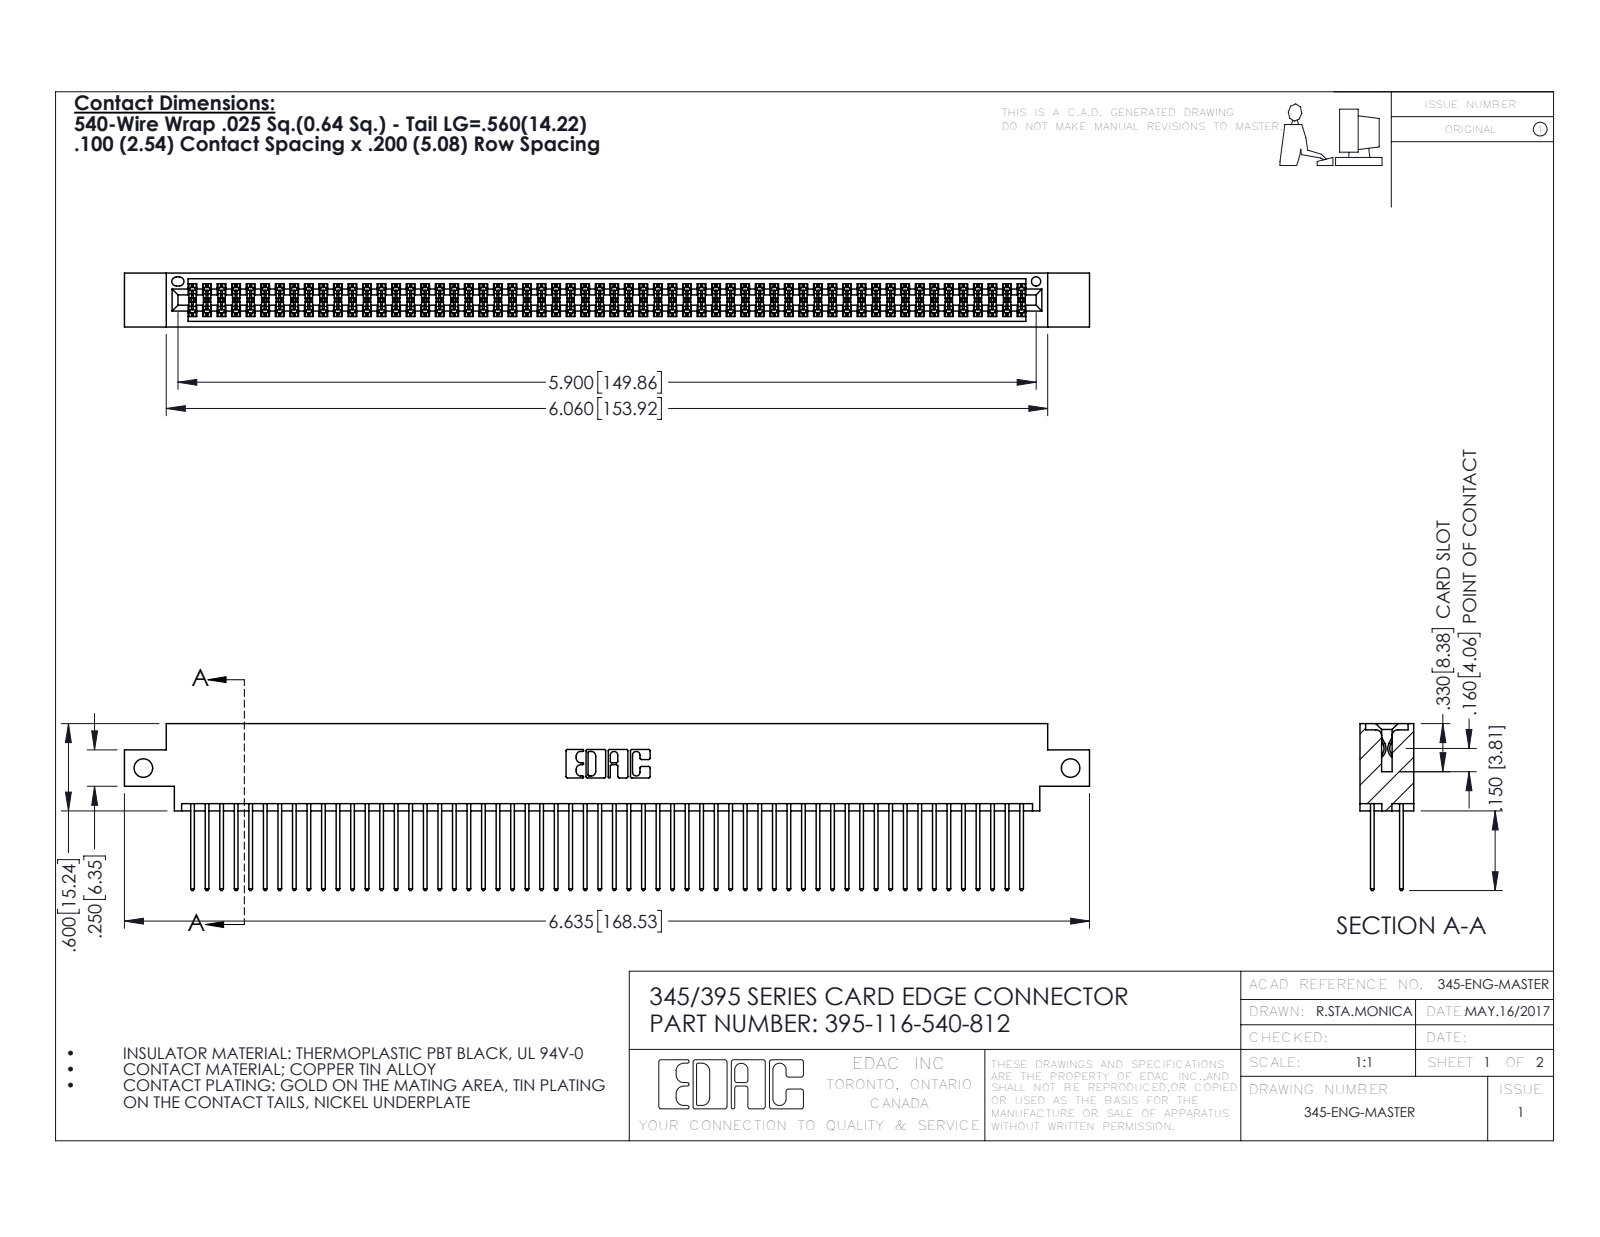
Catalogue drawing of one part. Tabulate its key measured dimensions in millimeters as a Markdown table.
| quantity | value |
| --- | --- |
| part name | 345-292-001_345-293-140; 345 Part_0.170 Offset - Side Mount; 395-116-540-812 |
| STEP written by | SolidWorks 2016 (CONFIG_CONTROL_DESIGN) |
| units | millimeters |
| bodies | 117 solids, 5930 faces (3912 planar, 2018 cylindrical, 0 other) |
| overall size | 168.5 × 29.1 × 9.4 |
| volume | 16 760 mm³ |
| surface area | 27 130 mm² |
| round holes (diameter × count) | 3.3 × 2, 1.6 × 1 |
| partial cylindrical surfaces (radius × count) | 0.2 × 174, 0.3 × 116, 0.3 × 22, 0.2 × 6, 0.8 × 6, 0.7 × 3, 0.4 × 2, 0.5 × 2 |
| main face-to-face distances | 1.8, 7.6, 5.1, 2.5, 6.9, 0.6, 9.4, 5.7, 4.4, 3.8 |
| hole center spacings | 161.9 |
